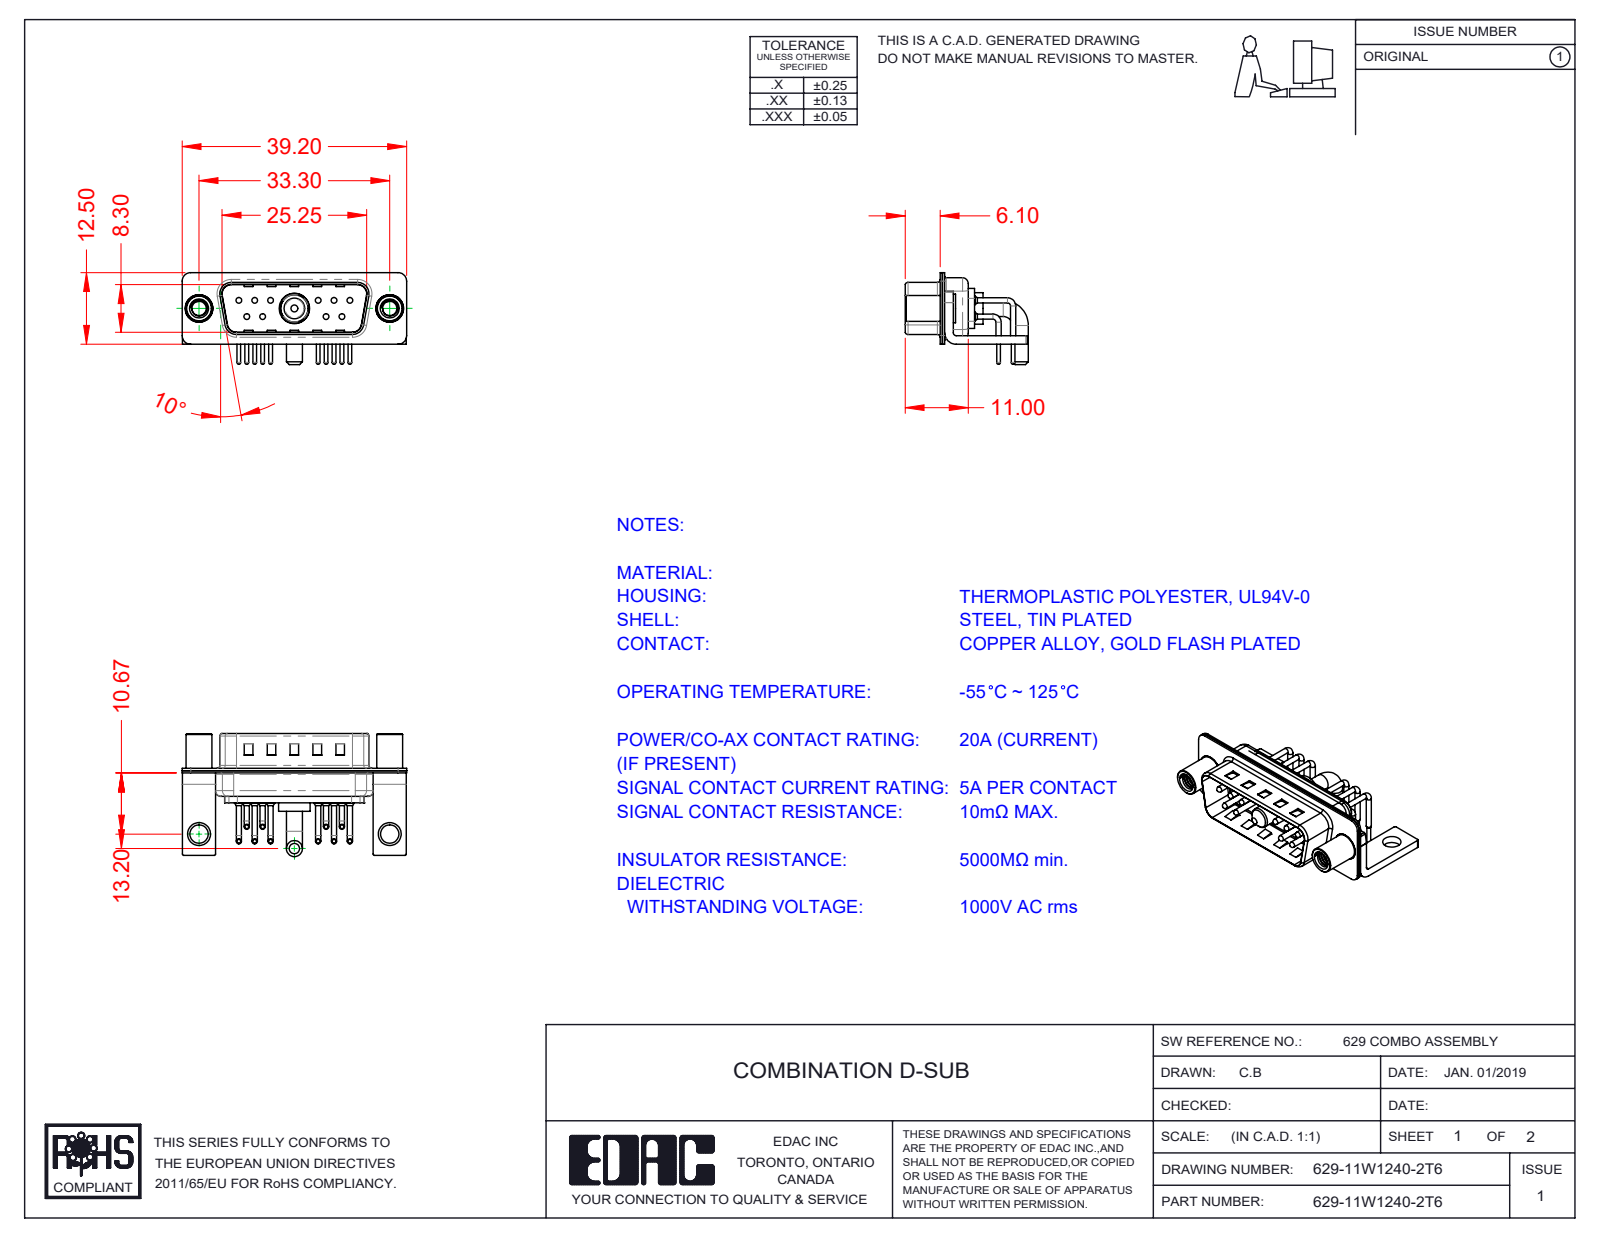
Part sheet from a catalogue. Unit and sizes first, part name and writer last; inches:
Units: inches
Overall size (bounding box): 1.543 × 0.846 × 0.632
Round holes (diameter × count): ⌀0.03 ×10, ⌀0.063 ×10, ⌀0.079 ×10, ⌀0.098 ×2, ⌀0.126 ×2, ⌀0.157 ×2, ⌀0.189 ×2, ⌀0.191 ×1, ⌀0.209 ×1
Round bosses / shafts (diameter × count): ⌀0.035 ×20, ⌀0.059 ×10, ⌀0.039 ×10, ⌀0.026 ×10, ⌀0.197 ×2, ⌀0.193 ×2, ⌀0.177 ×2, ⌀0.11 ×2
Partial cylindrical surfaces — rounded edges, fillets, slot ends (radius × count): R0.01 ×16, R0.059 ×16, R0.079 ×13, R0.04 ×10, R0.02 ×9, R0.063 ×8, R0.039 ×7, R0.024 ×4
Main face-to-face distances: 0.016, 0.031, 0.059, 0.374, 0.358, 0.343, 0.39, 0.024, 0.075, 0.205
Hole centre spacings: 0.124, 0.109, 0.545, 0.436, 0.654, 0.198, 0.198, 0.218
Volume: 0.149 in³ · Surface area: 9.545 in²
Bodies: 19 solids, 1594 faces (820 planar, 590 cylindrical, 184 other)
Part name (STEP PRODUCT): 629Combo Shell Rear_15 Contacts; Power Pin_20A RA; 629Combo Housing_11W1; 629Combo Contact Row 1 (+5 more)
STEP written by: SolidWorks 2020 (CONFIG_CONTROL_DESIGN)
